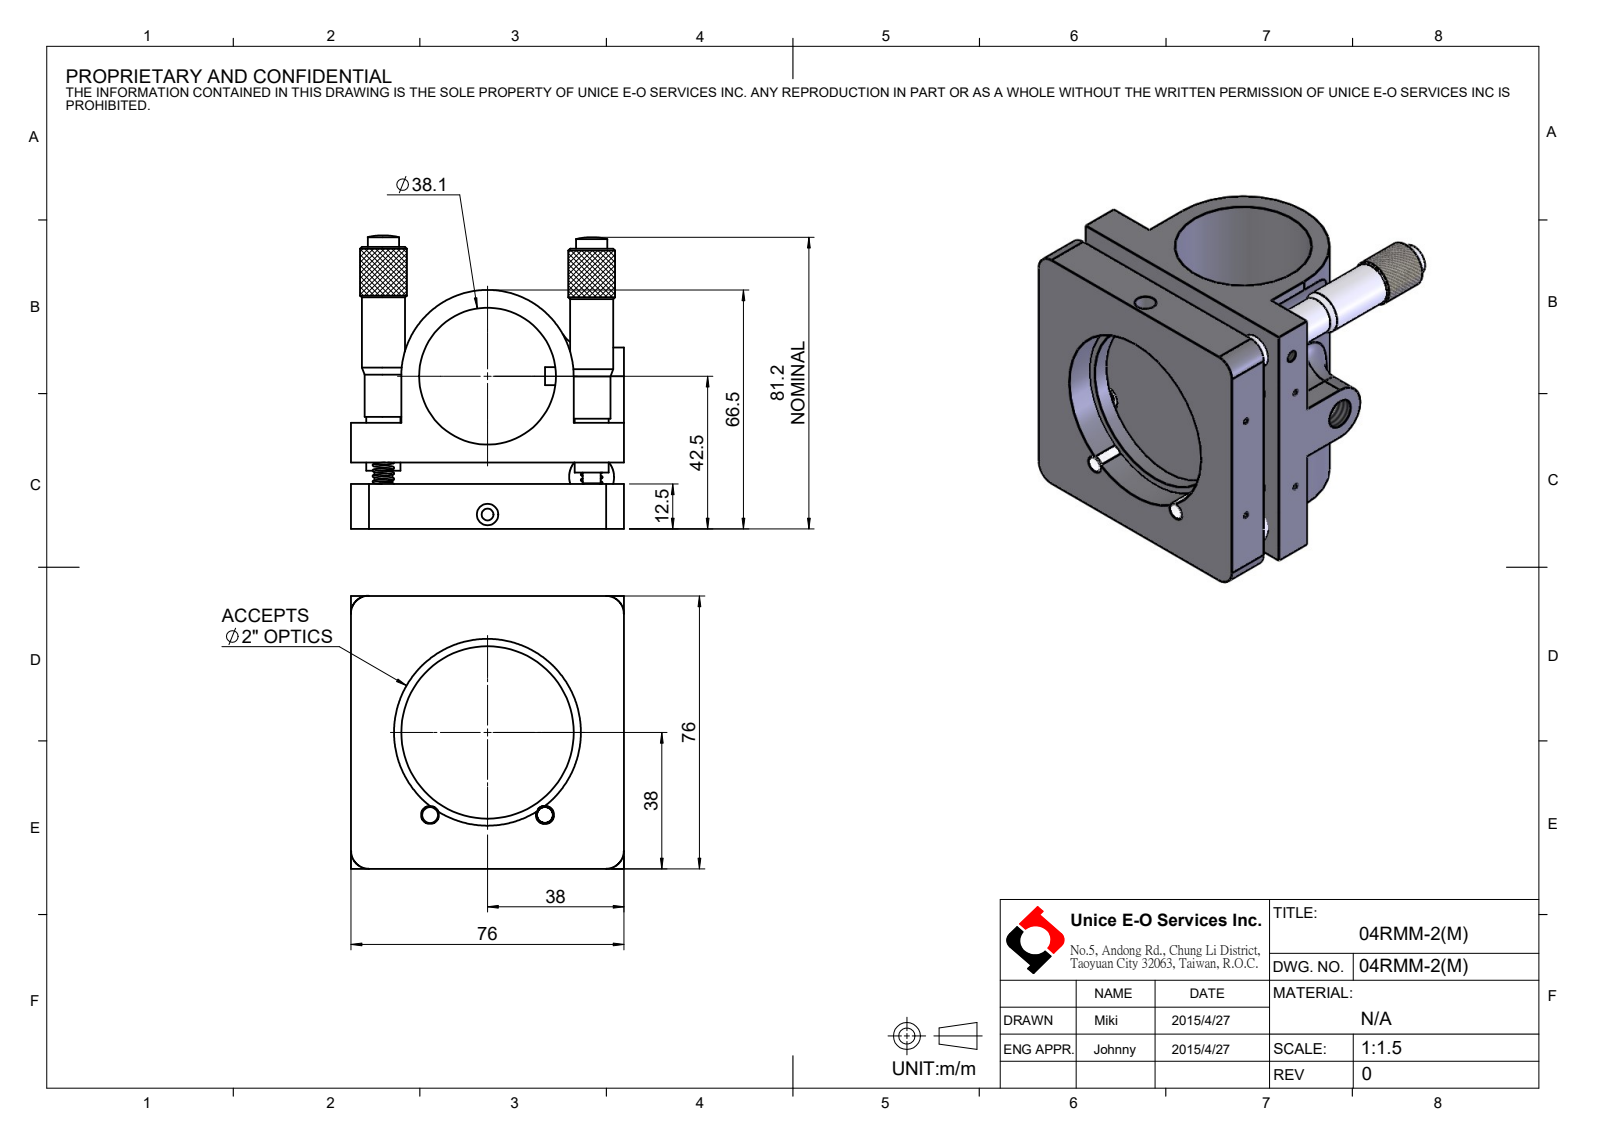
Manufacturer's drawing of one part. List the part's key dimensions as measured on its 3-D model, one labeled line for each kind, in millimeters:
Part name (STEP PRODUCT): 04RMM-2(M)
STEP written by: SolidWorks 2022 (CONFIG_CONTROL_DESIGN)
Units: millimetres
Bodies: 18 solids, 209 faces (91 planar, 77 cylindrical, 41 other)
Overall size (bounding box): 81.67 × 76 × 76
Volume: 153 754 mm³ · Surface area: 54 198 mm²
Round holes (diameter × count): ⌀1.2 ×4, ⌀1.7 ×4, ⌀3.3 ×3, ⌀6.3 ×3, ⌀7 ×3, ⌀5 ×2, ⌀9.6 ×2, ⌀6 ×1, ⌀8 ×1, ⌀8.5 ×1, ⌀38.1 ×1, ⌀48 ×1
Round bosses / shafts (diameter × count): ⌀0.6 ×6, ⌀1.6 ×4, ⌀5 ×3, ⌀13 ×2, ⌀12 ×2, ⌀10.5 ×2, ⌀9.5 ×2, ⌀8.7 ×2
Partial cylindrical surfaces — rounded edges, fillets, slot ends (radius × count): R8 ×5, R5 ×4, R24 ×1
Main face-to-face distances: 6, 76, 12.5, 18.5, 17, 11, 29.5, 14, 62, 48
Hole centre spacings: 32, 33.12, 13, 13.09, 14.76, 19.5, 22.2, 23.71
